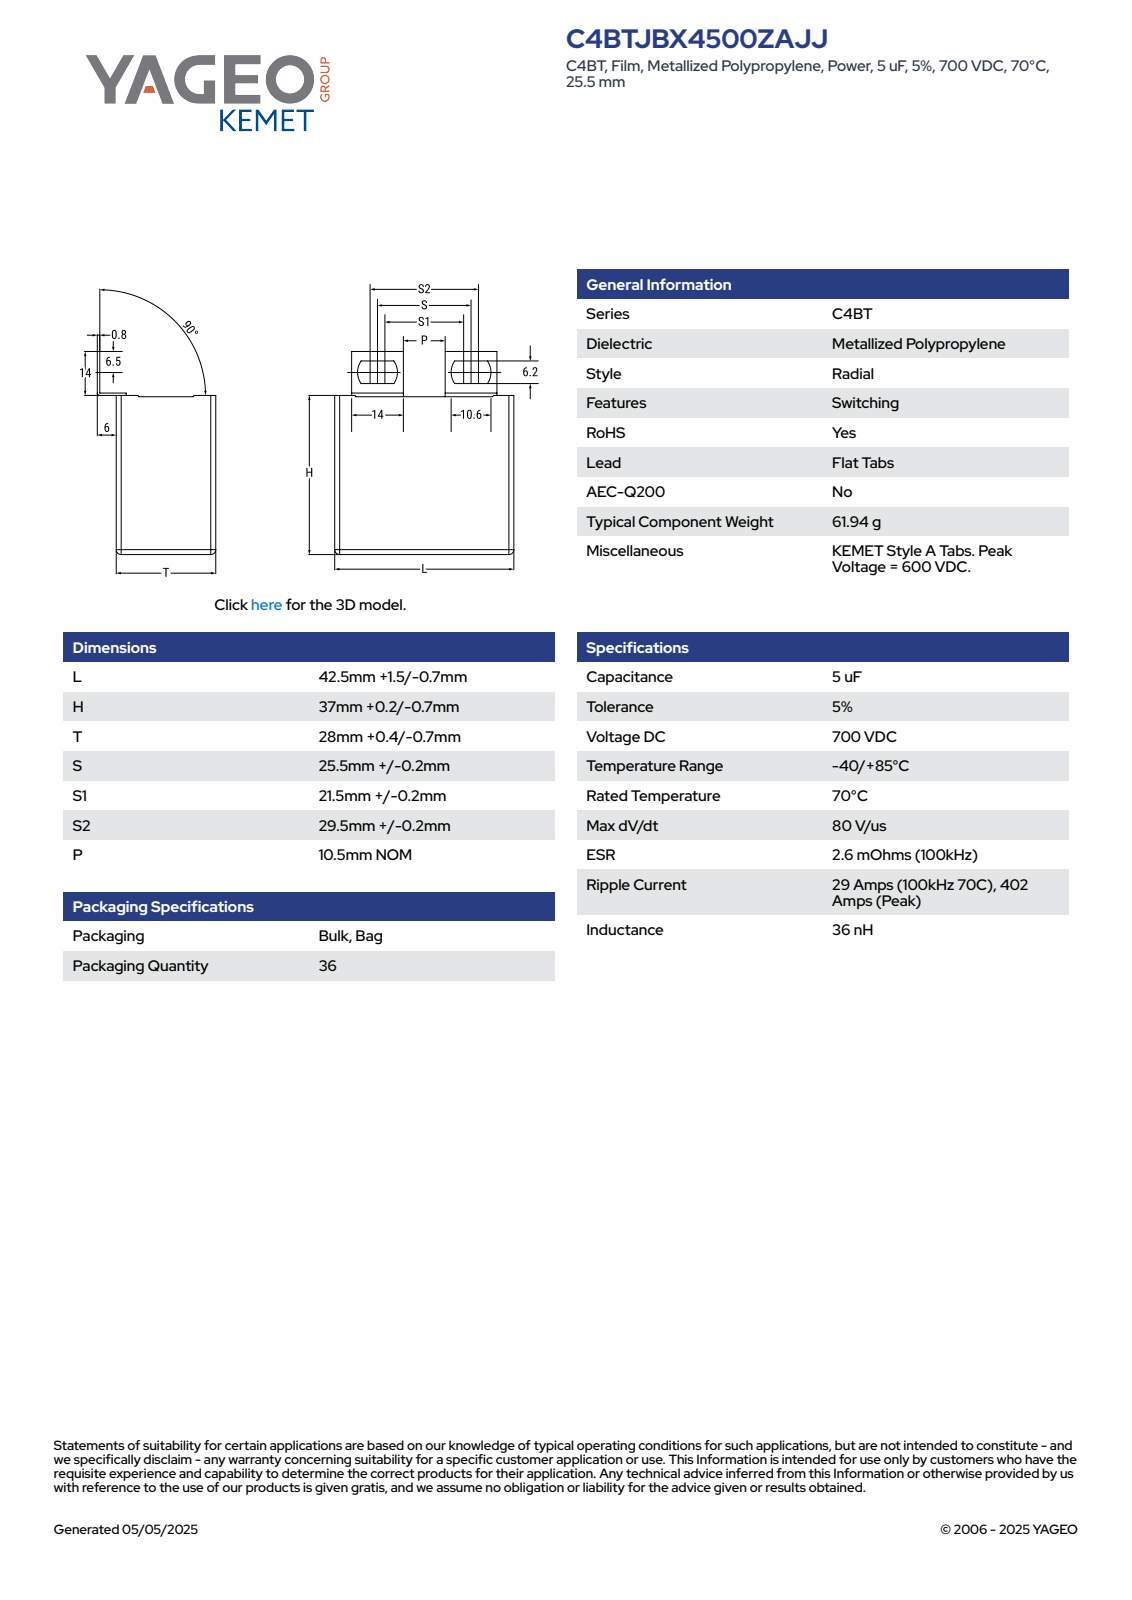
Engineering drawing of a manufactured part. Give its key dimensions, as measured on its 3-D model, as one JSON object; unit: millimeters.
{"part_name": "CFP_C4BA_42.5X37X28_L42.5H37T28S25.7", "step_written_by": "SolidWorks 2014 (AUTOMOTIVE_DESIGN)", "units": "millimeters", "bodies": {"solids": 4, "faces": 97, "planar": 91, "cylindrical": 6, "other": 0}, "overall_size": [51.6, 42.5, 34.01], "volume_mm3": 44411, "surface_area_mm2": 9328, "partial_cylinders_radius": [[6.1, 4]], "face_to_face_distances": [28, 36.95, 42.5, 0.6, 37, 37.6, 0.65, 34, 6, 33.4]}
